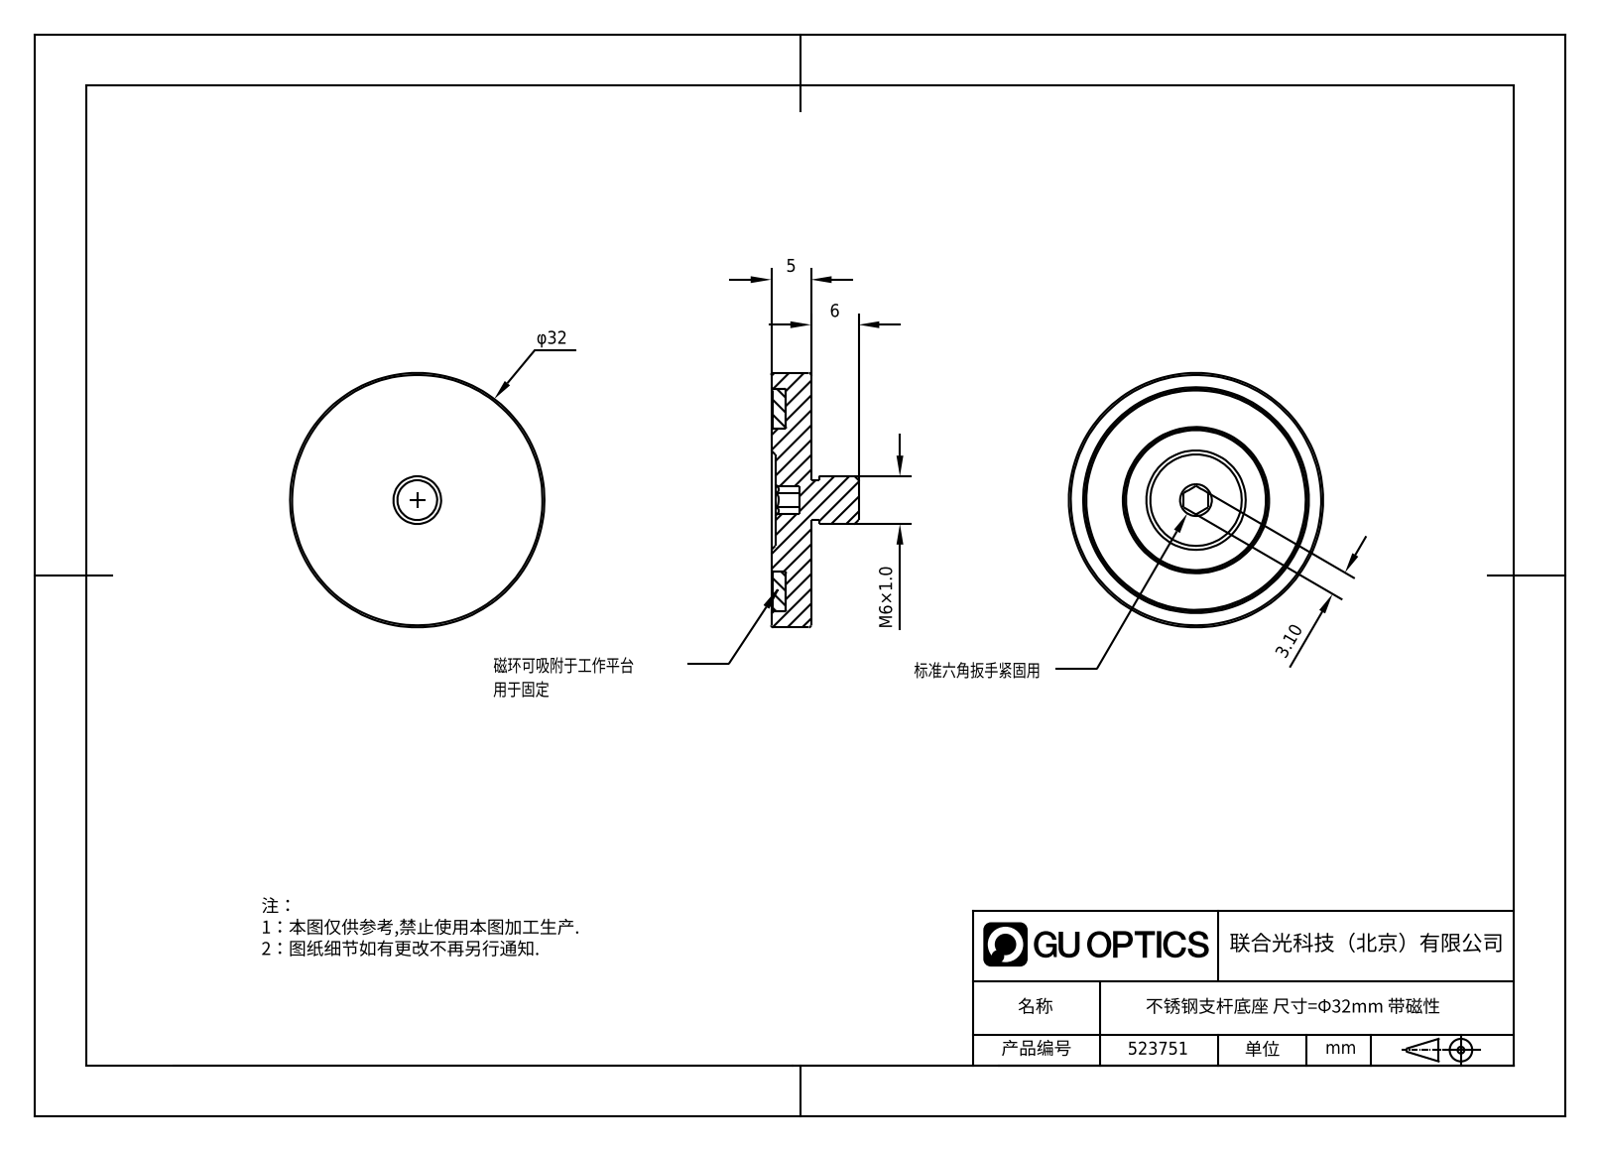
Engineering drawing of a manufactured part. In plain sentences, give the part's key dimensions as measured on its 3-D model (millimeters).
The part is named "523751". Its 3-D file was written by "SolidWorks 2020 (CONFIG_CONTROL_DESIGN)". It is 2 solids with 34 faces: 16 planar, 7 cylindrical and 11 other. Overall it measures 32 by 32 by 11 millimeters. Its volume is 4 035 cubic millimeters and its surface area 3 442 square millimeters. Round holes: 1 of diameter 18, 1 of diameter 28. Round bosses or shafts: 1 of diameter 32, 1 of diameter 6, 1 of diameter 5. The main face-to-face distances are 3.15, 1.7, 4.85, 5, 1.85, 0.5, 0.35, 1.35, 4.5, 6.
